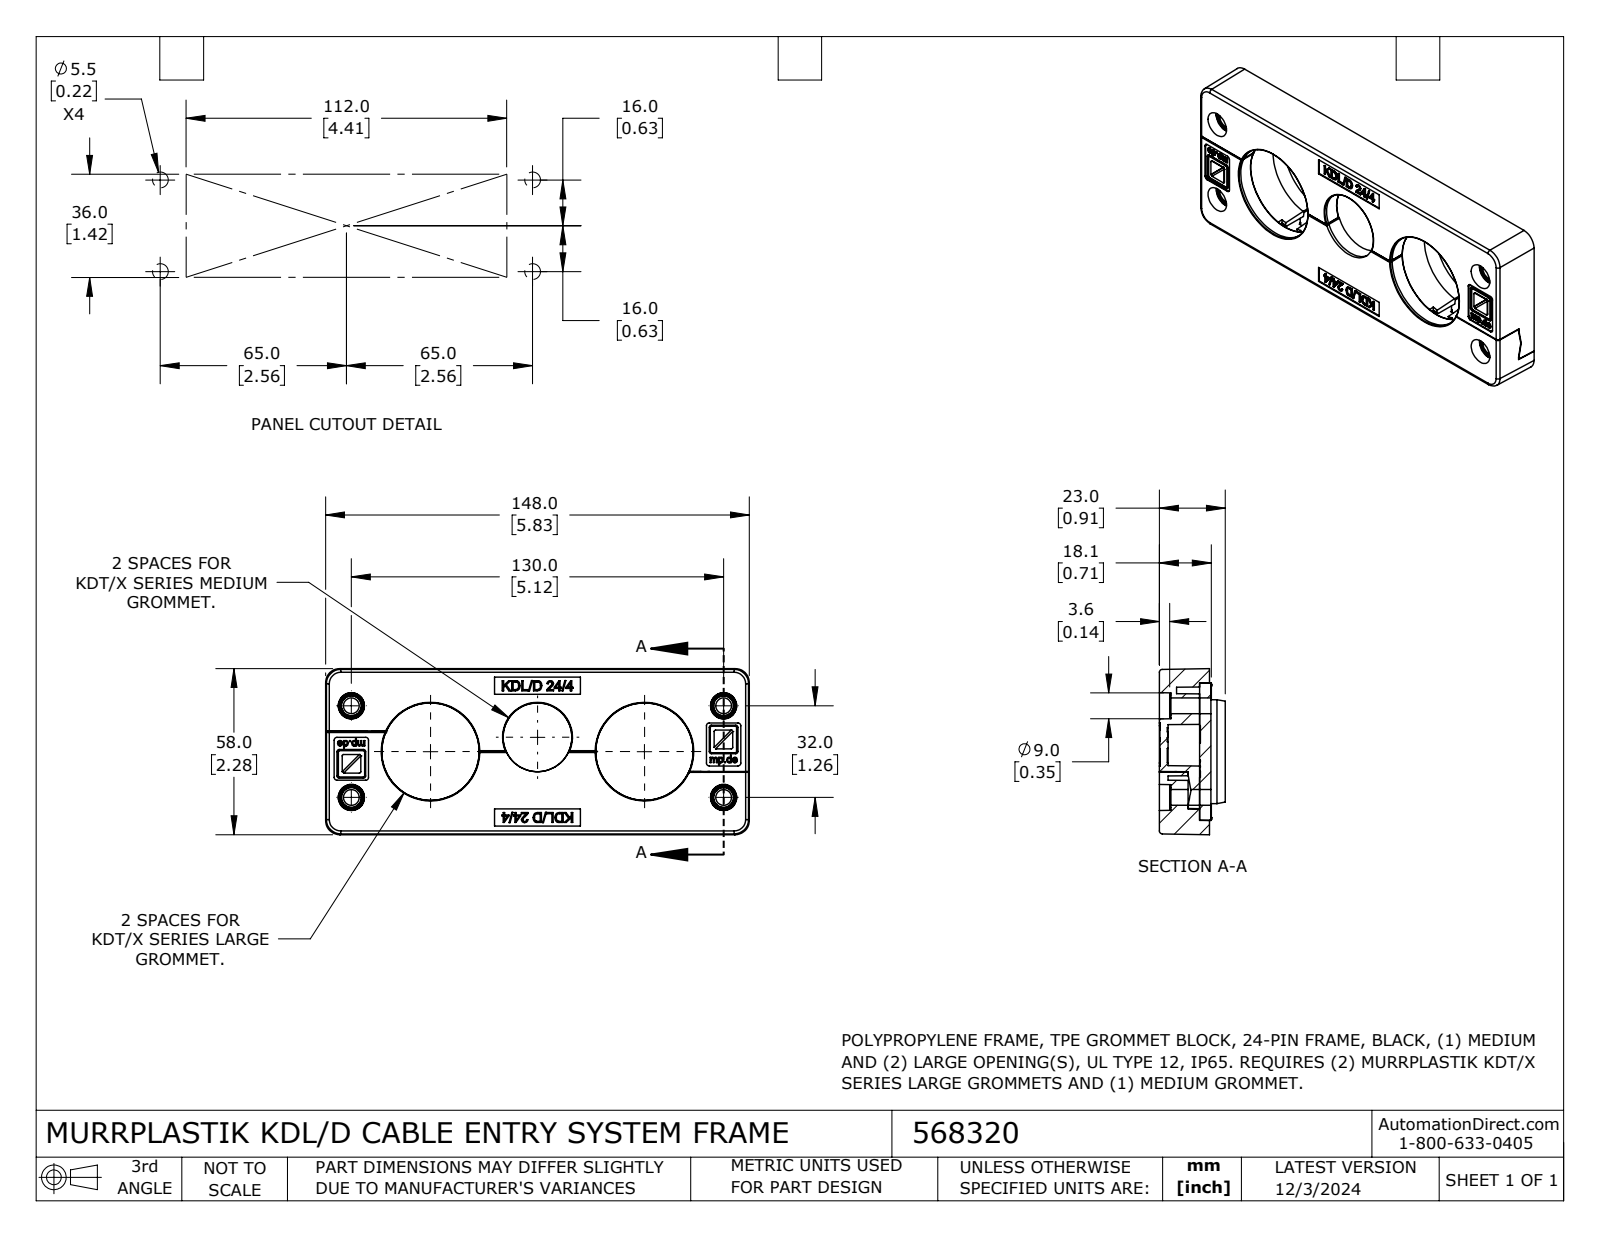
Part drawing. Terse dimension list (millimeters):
name: 568320
written by: SolidWorks 2023 (CONFIG_CONTROL_DESIGN)
unit: mm
bodies: 3 solids, 1209 faces (648 planar, 177 cylindrical, 384 other)
size: 148 × 58 × 23
volume: 102 500 mm³; area: 52 640 mm²
holes: 4× ⌀5, 4× ⌀5.5, 2× ⌀6, 2× ⌀35, 1× ⌀24.9
rounds: 24× R1, 20× R0.2, 20× R0.5, 12× R0.4, 8× R0.8, 4× R0.1, 4× R0.2, 4× R0.3
face distances: 6, 12, 18, 0.5, 4, 11.5, 17.5, 14, 3.5, 8
hole spacings: 31.9, 103.6, 65.9, 7.3, 10, 10.1, 14.6, 17.4
